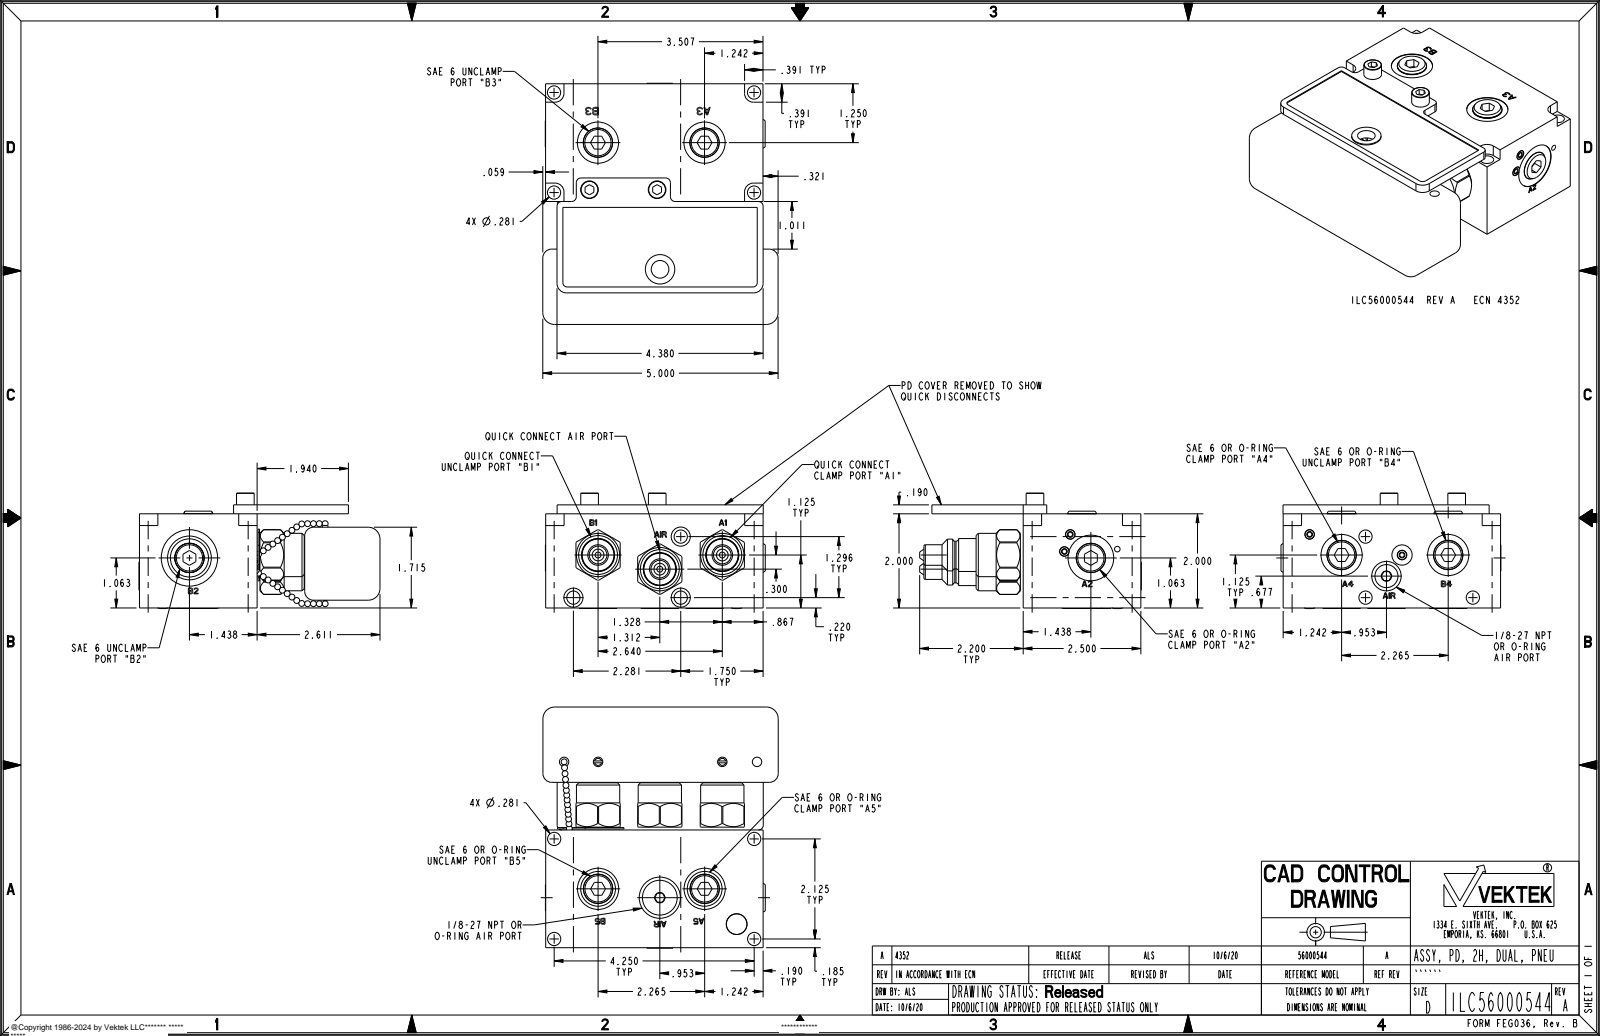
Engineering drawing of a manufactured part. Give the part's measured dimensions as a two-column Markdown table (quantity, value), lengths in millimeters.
| quantity | value |
| --- | --- |
| part name | ILC56000544_PD; ILC56000530_COVER; ILC56000544 |
| STEP written by | PRO/ENGINEER BY PARAMETRIC TECHNOLOGY CORPORATION, 2013320 (CONFIG_CONTROL_DESIGN) |
| units | millimeters |
| bodies | 6 solids, 1573 faces (952 planar, 207 cylindrical, 414 other) |
| overall size | 130.1 × 127 × 62.4 |
| volume | 421 500 mm³ |
| surface area | 104 500 mm² |
| round holes (diameter × count) | 7.1 × 8, 22.2 × 5, 3.1 × 4, 5.1 × 4, 10.3 × 3, 13.1 × 3, 2 × 2, 5.1 × 2, 5.1 × 2, 3 × 1, 5.7 × 1, 9.5 × 1 |
| round bosses / shafts (diameter × count) | 5 × 4, 4.5 × 4, 23.4 × 3, 17.8 × 3, 17.1 × 3, 14.9 × 3, 11.1 × 3, 9.5 × 2 |
| partial cylindrical surfaces (radius × count) | 4.7 × 8, 6.4 × 8, 2.5 × 6, 13.6 × 3, 2.3 × 2, 5.1 × 2, 6 × 1, 14 × 1 |
| main face-to-face distances | 50.8, 63.5, 4.3, 55.1, 43.6, 7.2, 11.6, 4.2, 39.4, 46.6 |
| hole center spacings | 40.8, 54, 55.6, 57.5, 67.1, 74.1, 108, 120.7 |
